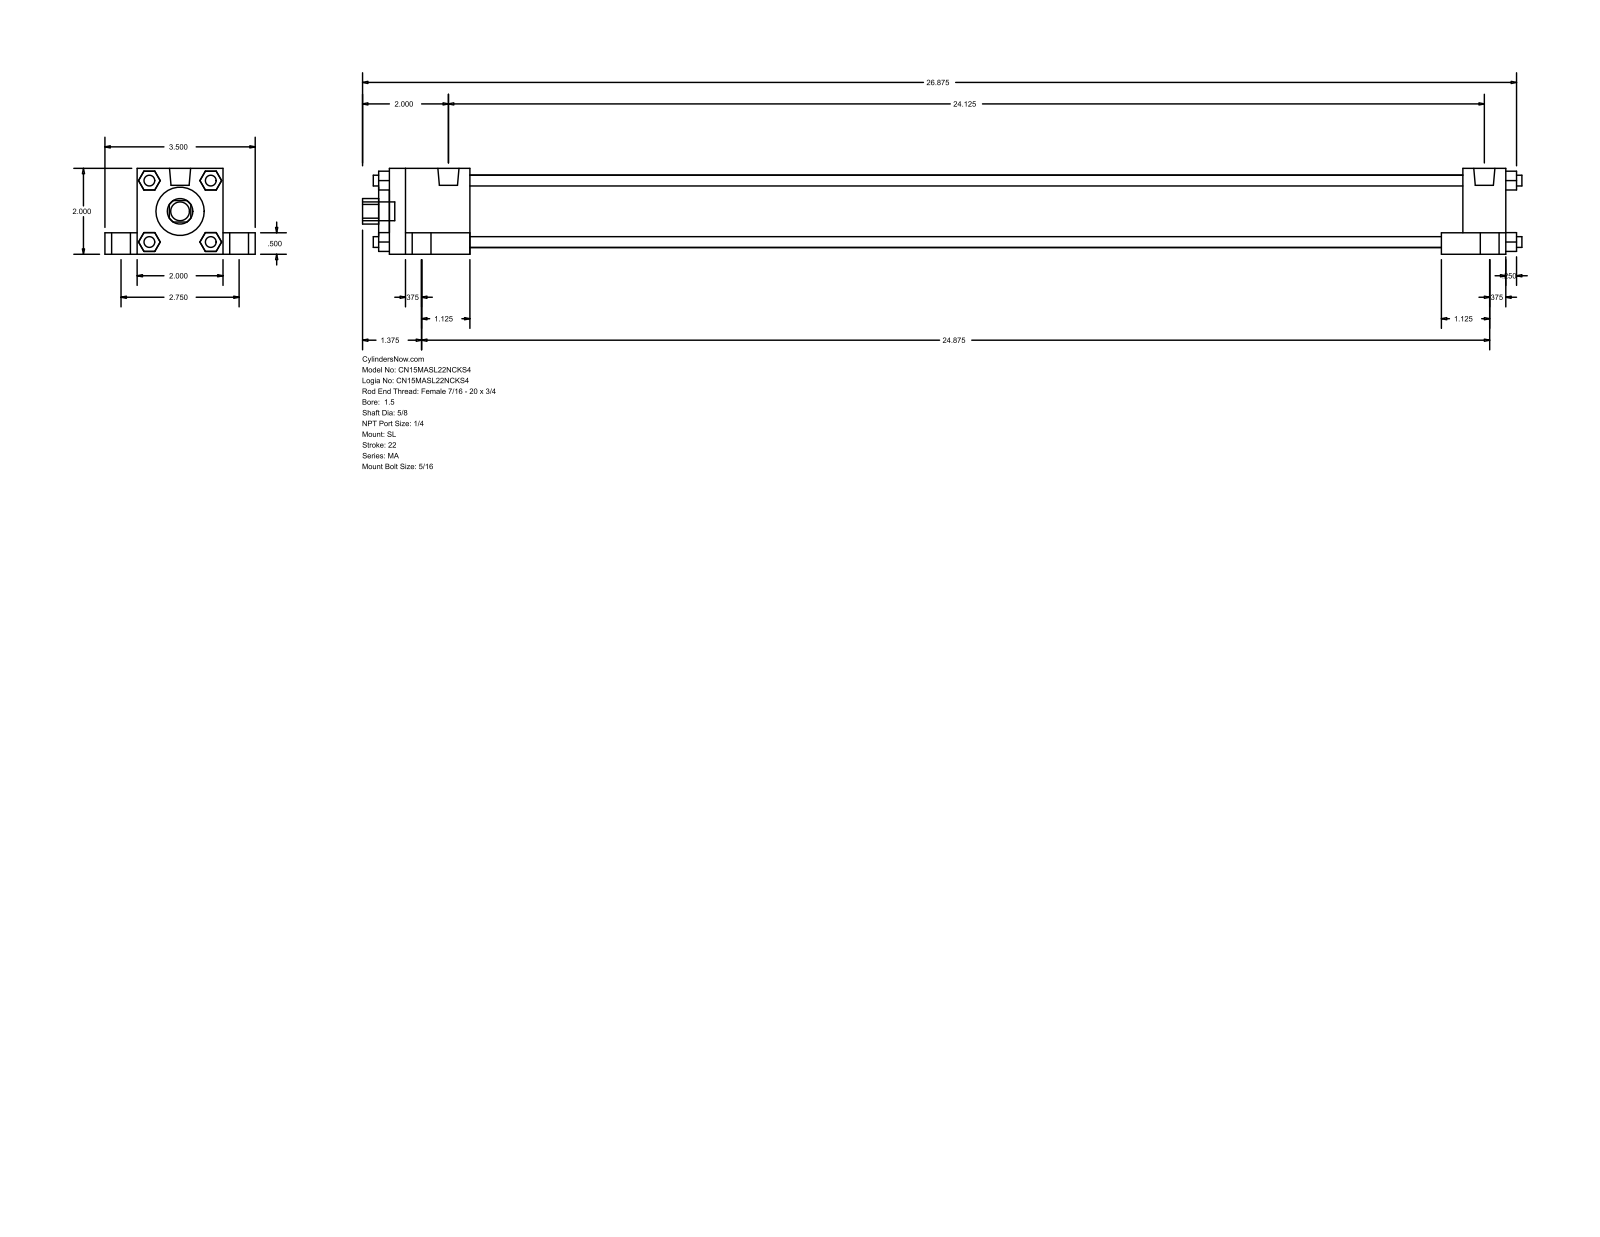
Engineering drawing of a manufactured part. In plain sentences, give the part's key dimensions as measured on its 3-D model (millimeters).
The part is named "MA_SL__0150_0.625". Its 3-D file was written by "GSSL Pune (CONFIG_CONTROL_DESIGN)". It is 0 solids with 148 faces: 112 planar, 36 cylindrical and 0 other. Overall it measures 685.8 by 88.9 by 50.8 millimeters. Round holes: 1 of diameter 15.88, 1 of diameter 28.57, 1 of diameter 42.93. Round bosses or shafts: 5 of diameter 11.11, 4 of diameter 17.46, 4 of diameter 7.94, 4 of diameter 6.35, 2 of diameter 12.49. Partial cylindrical surfaces (rounded edges, fillets, slot ends): 1 of radius 7.54. The main face-to-face distances are 50.8, 19.05, 38.1, 12.7, 69.85, 660.39, 6.35, 9.52, 666.74, 635.
